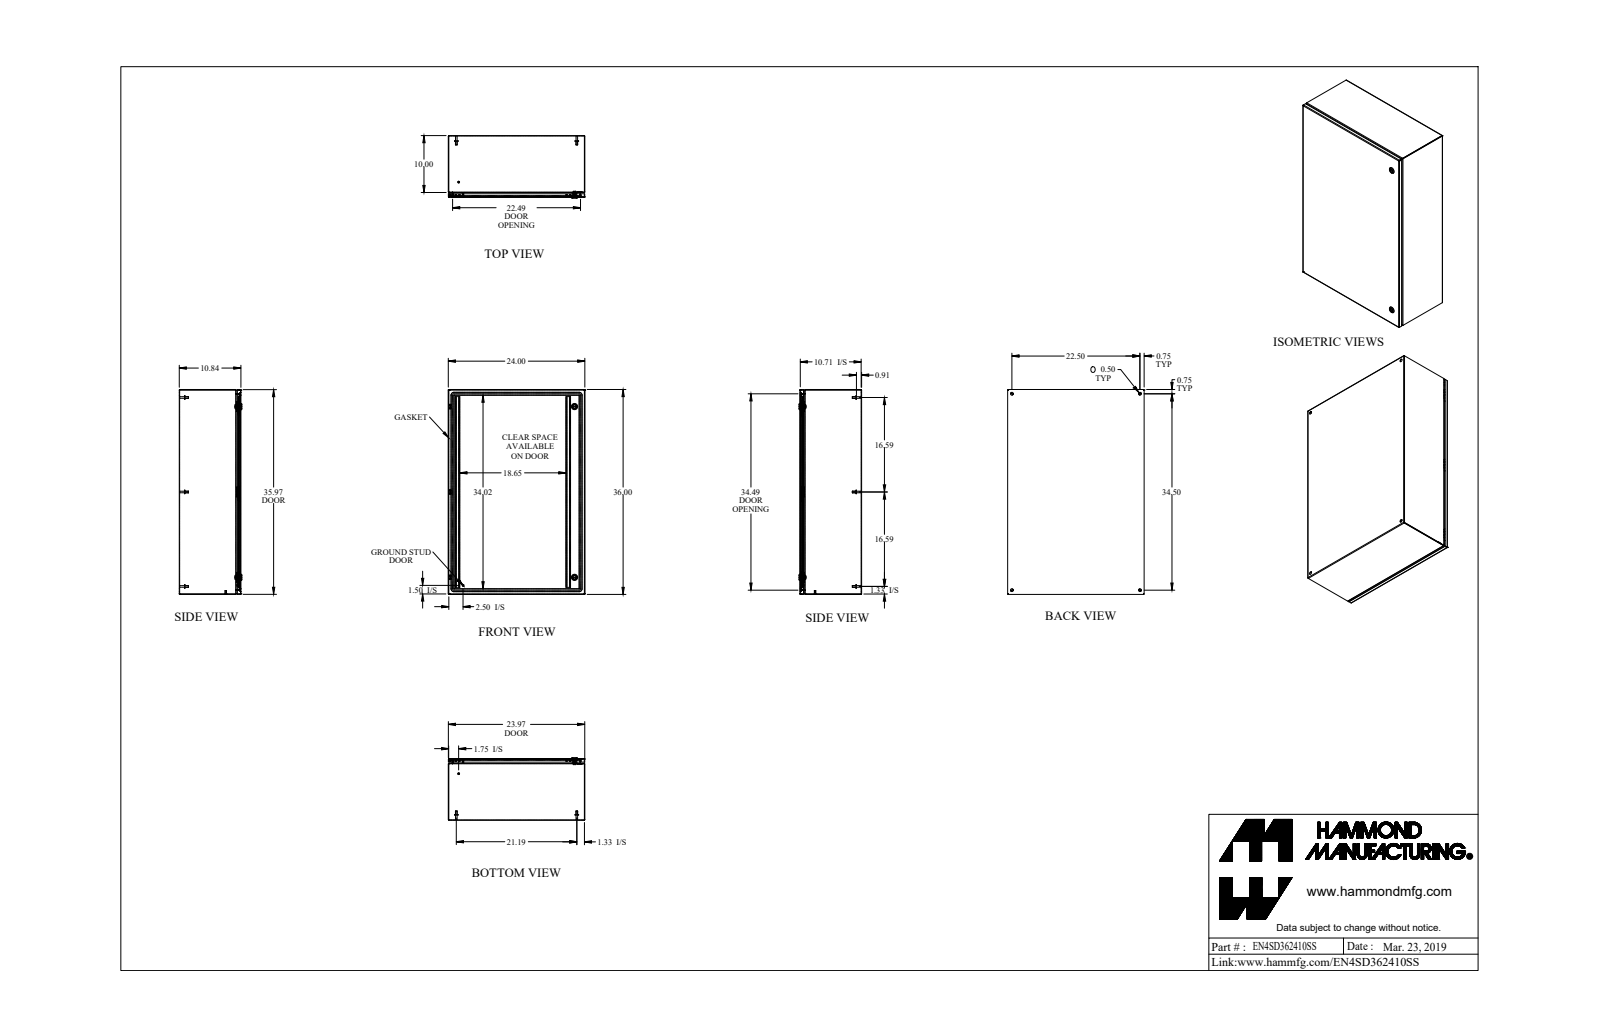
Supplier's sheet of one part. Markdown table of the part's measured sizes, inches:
| quantity | value |
| --- | --- |
| part name | EN4SD362410SS |
| STEP written by | SolidWorks 2019 (AUTOMOTIVE_DESIGN) |
| units | inches |
| bodies | 35 solids, 959 faces (458 planar, 313 cylindrical, 188 other) |
| overall size | 36 × 24 × 11.002 |
| volume | 244.1 in³ |
| surface area | 6 859 in² |
| round holes (diameter × count) | 0.5 × 6, 0.197 × 2, 0.387 × 2, 0.63 × 2, 0.768 × 2, 0.172 × 1, 0.24 × 1, 0.242 × 1 |
| round bosses / shafts (diameter × count) | 0.625 × 8, 0.313 × 8, 0.275 × 6, 1.1 × 2, 0.785 × 2, 0.525 × 2, 0.25 × 2, 0.236 × 2 |
| partial cylindrical surfaces (radius × count) | 0.036 × 20, 0.108 × 20, 0.25 × 16, 0.01 × 12, 0.048 × 12, 0.006 × 6, 0.062 × 6, 0.125 × 4 |
| main face-to-face distances | 0.072, 10.77, 10.698, 10.842, 23.928, 35.928, 23.856, 24, 35.856, 36 |
| hole center spacings | 2.488, 21.557, 22.5, 32.267, 34.5, 38.726, 41.189, 30 |
